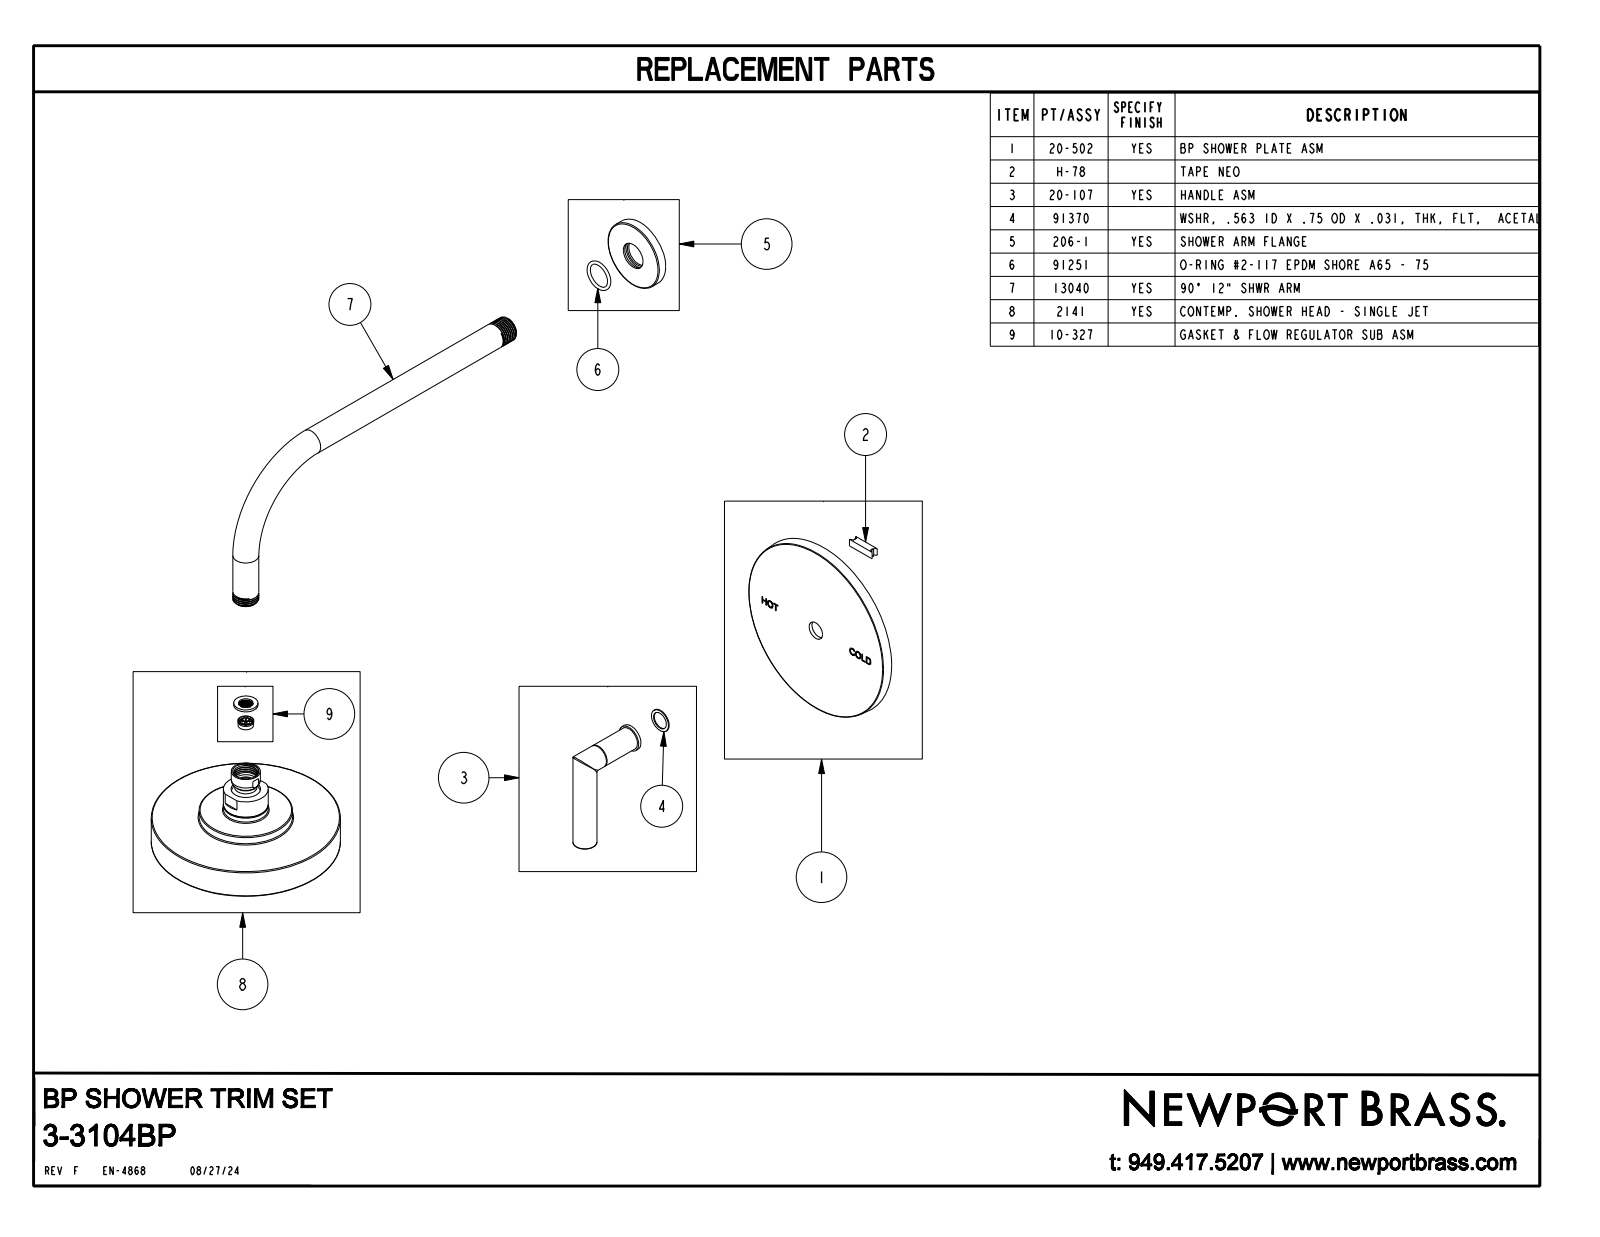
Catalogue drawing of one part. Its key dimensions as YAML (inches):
part_name: "3-3104BP"
step_written_by: "CREO PARAMETRIC BY PTC INC, 2018400 (CONFIG_CONTROL_DESIGN)"
units: inches
bodies: {solids: 2, faces: 987, planar: 157, cylindrical: 214, other: 616}
overall_size: [16.125, 13.799, 6]
volume: 54.67
surface_area: 206.7
round_holes:
  - {diameter: 0.05, count: 90}
  - {diameter: 0.22, count: 1}
  - {diameter: 5.256, count: 1}
round_bosses_or_shafts:
  - {diameter: 0.813, count: 2}
  - {diameter: 0.75, count: 2}
  - {diameter: 5.91, count: 1}
  - {diameter: 5.22, count: 1}
  - {diameter: 2.92, count: 1}
  - {diameter: 2.25, count: 1}
  - {diameter: 1.4, count: 1}
  - {diameter: 0.905, count: 1}
face_to_face_distances: [0.35, 0.291, 0.31, 0.04, 1.084, 0.793, 8.928, 9.219, 10.013, 0.031]
hole_center_spacings: [0.98, 1.41, 0.55, 0.851, 1.893, 0.43, 0.476, 0.912]
